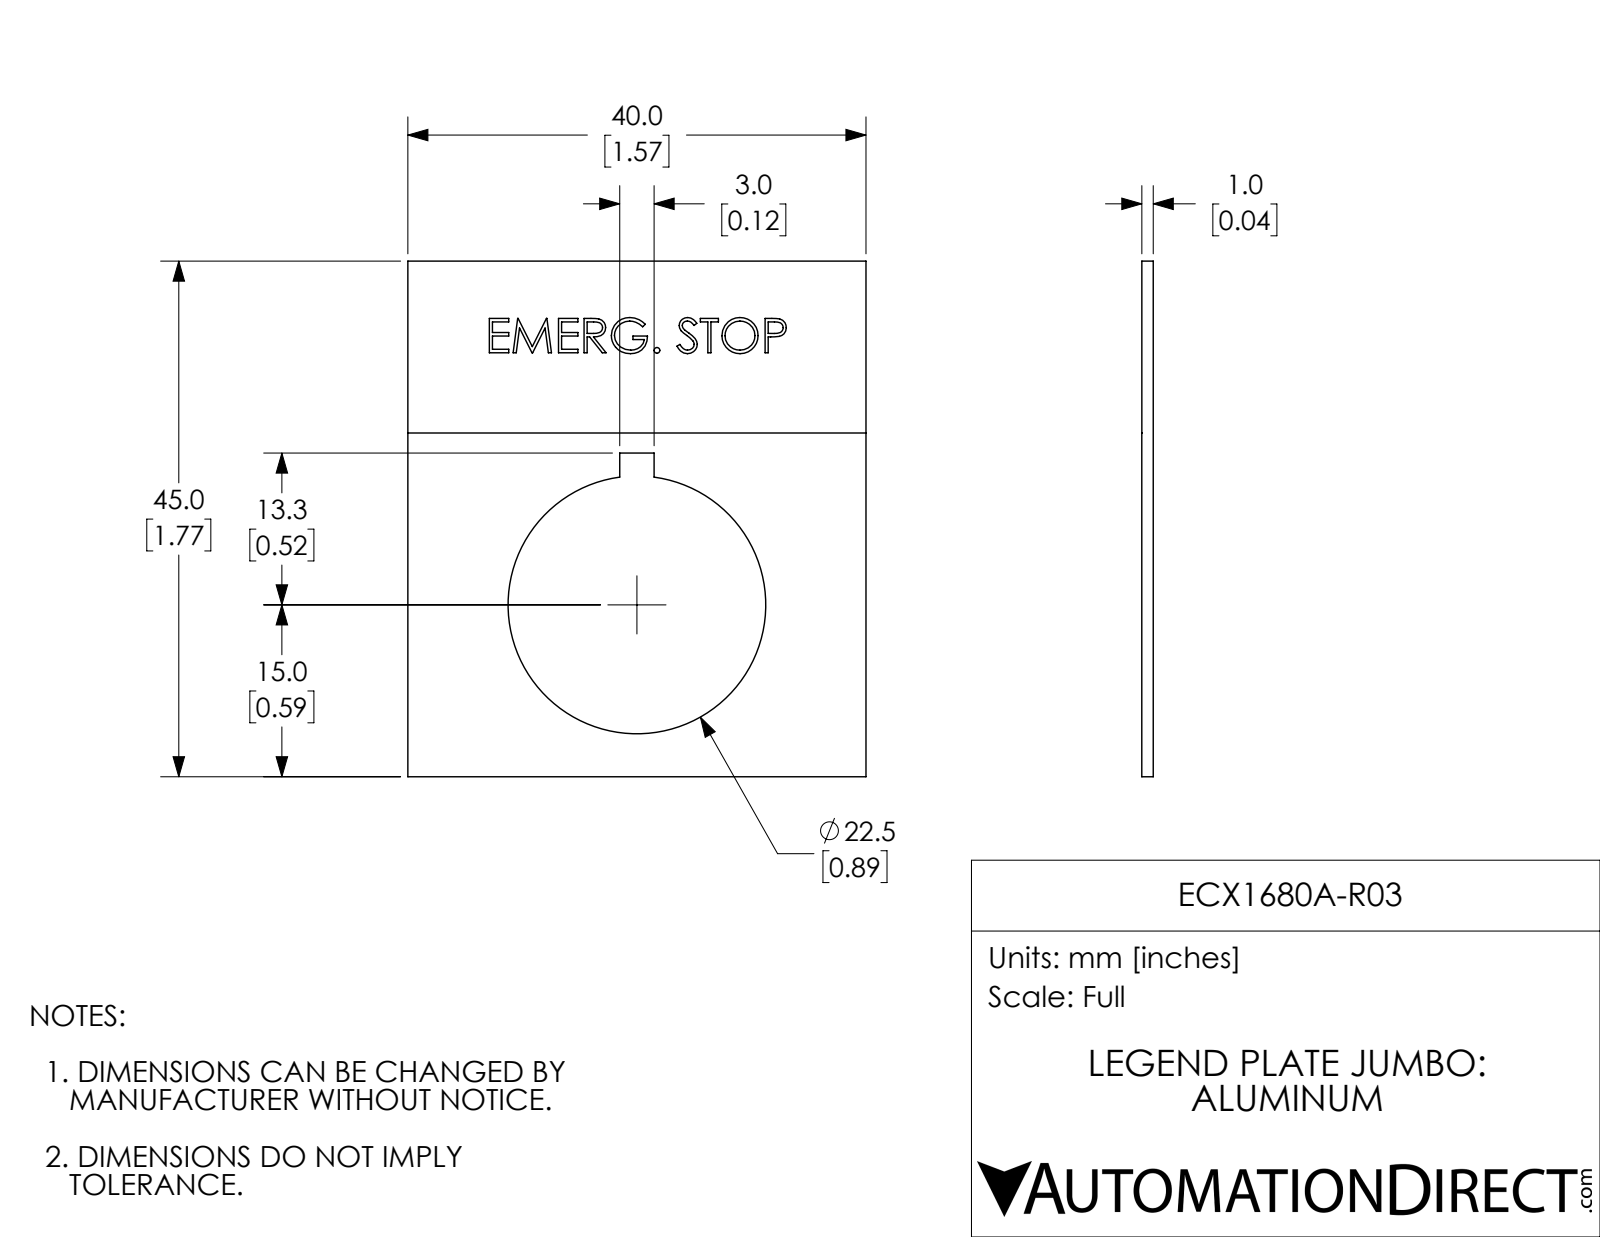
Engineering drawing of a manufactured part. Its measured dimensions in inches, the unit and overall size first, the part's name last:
Units: inches
Overall size (bounding box): 1.772 × 1.575 × 0.039
Round holes (diameter × count): ⌀0.886 ×1
Main face-to-face distances: 0.039, 0.039, 1.575, 1.772, 0.728, 0.846, 1.112, 0.659, 0.118, 1.181
Volume: 0.085 in³ · Surface area: 4.709 in²
Bodies: 1 solid, 144 faces (94 planar, 3 cylindrical, 47 other)
Part name (STEP PRODUCT): ECX1680A-R03
STEP written by: SolidWorks 2017 (AUTOMOTIVE_DESIGN)
